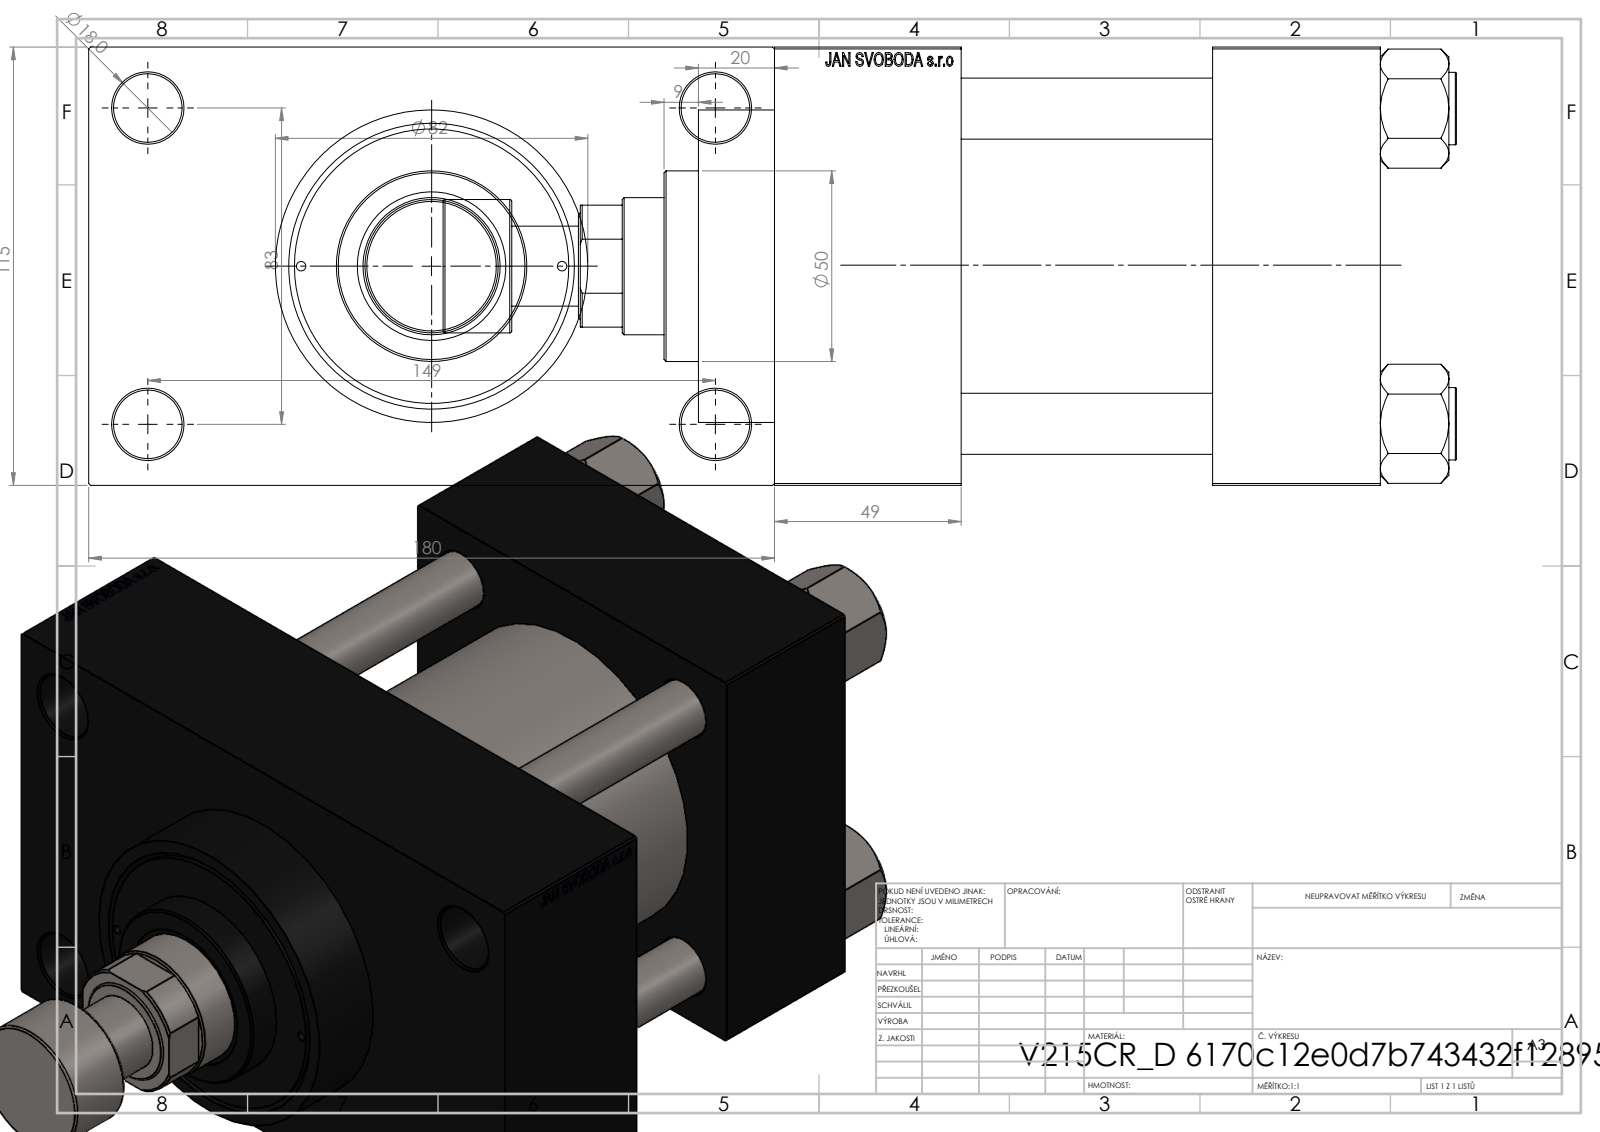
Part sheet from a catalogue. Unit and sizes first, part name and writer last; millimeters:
Units: millimetres
Overall size (bounding box): 266 × 180 × 115
Round holes (diameter × count): ⌀16 ×4, ⌀18 ×4, ⌀2.5 ×2, ⌀7 ×2, ⌀26.44 ×2, ⌀35 ×2, ⌀25.5 ×1, ⌀36 ×1, ⌀39 ×1, ⌀61 ×1, ⌀72 ×1, ⌀80 ×1
Round bosses / shafts (diameter × count): ⌀19 ×4, ⌀86 ×1, ⌀82 ×1, ⌀50 ×1, ⌀35 ×1, ⌀21 ×1
Main face-to-face distances: 115, 66, 49, 110, 44, 159, 32.5, 147.5, 20, 69
Hole centre spacings: 33.15, 41.96, 57.81, 58.48, 82.7, 85.28, 86.17, 89.24
Volume: 2 003 000 mm³ · Surface area: 302 044 mm²
Bodies: 12 solids, 1173 faces (551 planar, 96 cylindrical, 526 other)
Part name (STEP PRODUCT): V215CR_D_Body; V215CR_ROD_END_F; NUT_M5_D; V215CR_VCP_D (+2 more)
STEP written by: SolidWorks 2019 (CONFIG_CONTROL_DESIGN)
